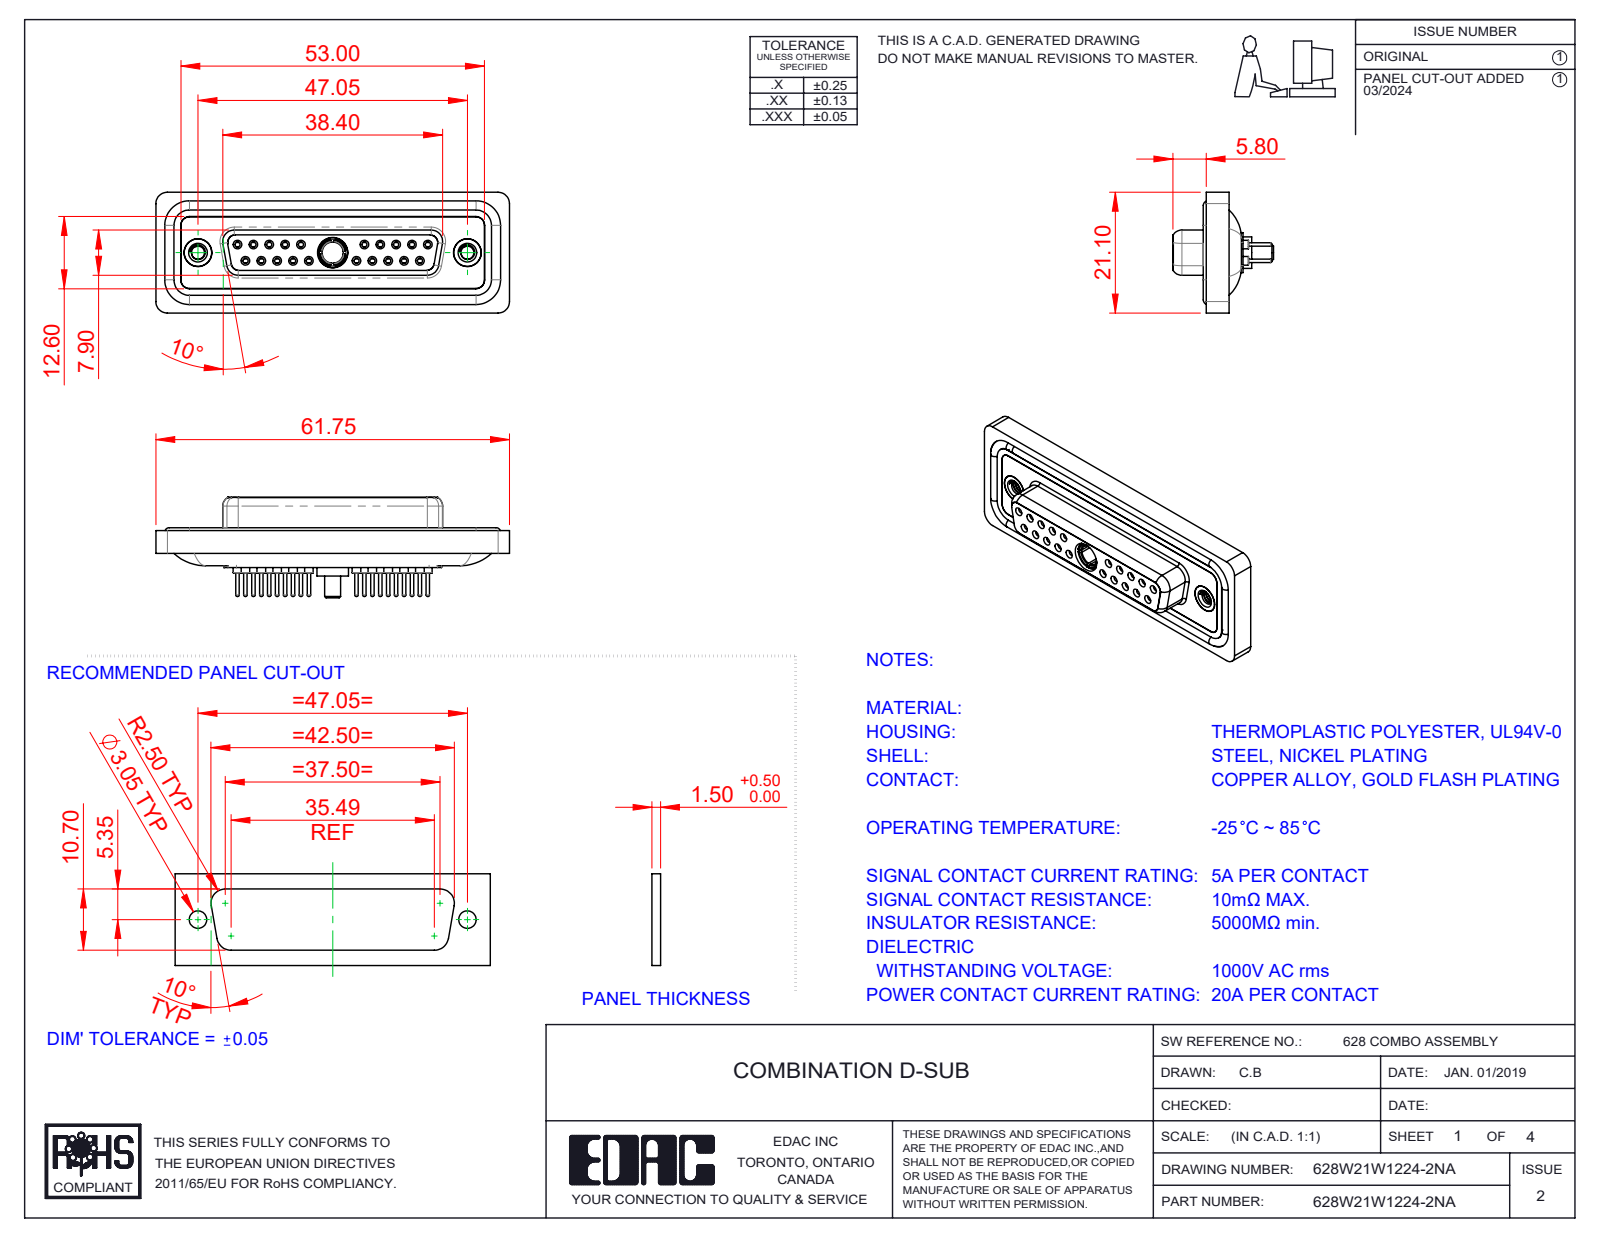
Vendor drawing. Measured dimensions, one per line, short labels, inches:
name: 628Combo Shell Front_25 Contacts; Power Socket_20A S; 628Combo Housing_21W1; 628Combo Contact Row 1_24 (+5 more)
written by: SolidWorks 2023 (CONFIG_CONTROL_DESIGN)
unit: in
bodies: 29 solids, 1558 faces (434 planar, 593 cylindrical, 531 other)
size: 2.431 × 0.831 × 0.691
volume: 0.511 in³; area: 21.7 in²
holes: 20× ⌀0.035, 20× ⌀0.043, 20× ⌀0.059, 20× ⌀0.079, 10× ⌀0.063, 10× ⌀0.067, 3× ⌀0.191, 2× ⌀0.089, 2× ⌀0.157, 2× ⌀0.159, 2× ⌀0.197, 1× ⌀0.146
bosses: 20× ⌀0.087, 20× ⌀0.024, 14× ⌀0.063, 2× ⌀0.195, 2× ⌀0.189, 1× ⌀0.217, 1× ⌀0.205, 1× ⌀0.195
rounds: 22× R0.059, 18× R0.079, 8× R0.053, 8× R0.063, 4× R0.01, 4× R0.02, 4× R0.024, 4× R0.026
face distances: 0.016, 0.071, 0.293, 0.26, 0.222, 0.02, 0.063, 0.278, 0.114, 0.043
hole spacings: 0.124, 0.109, 0.218, 0.198, 0.327, 0.294, 0.654, 0.763
